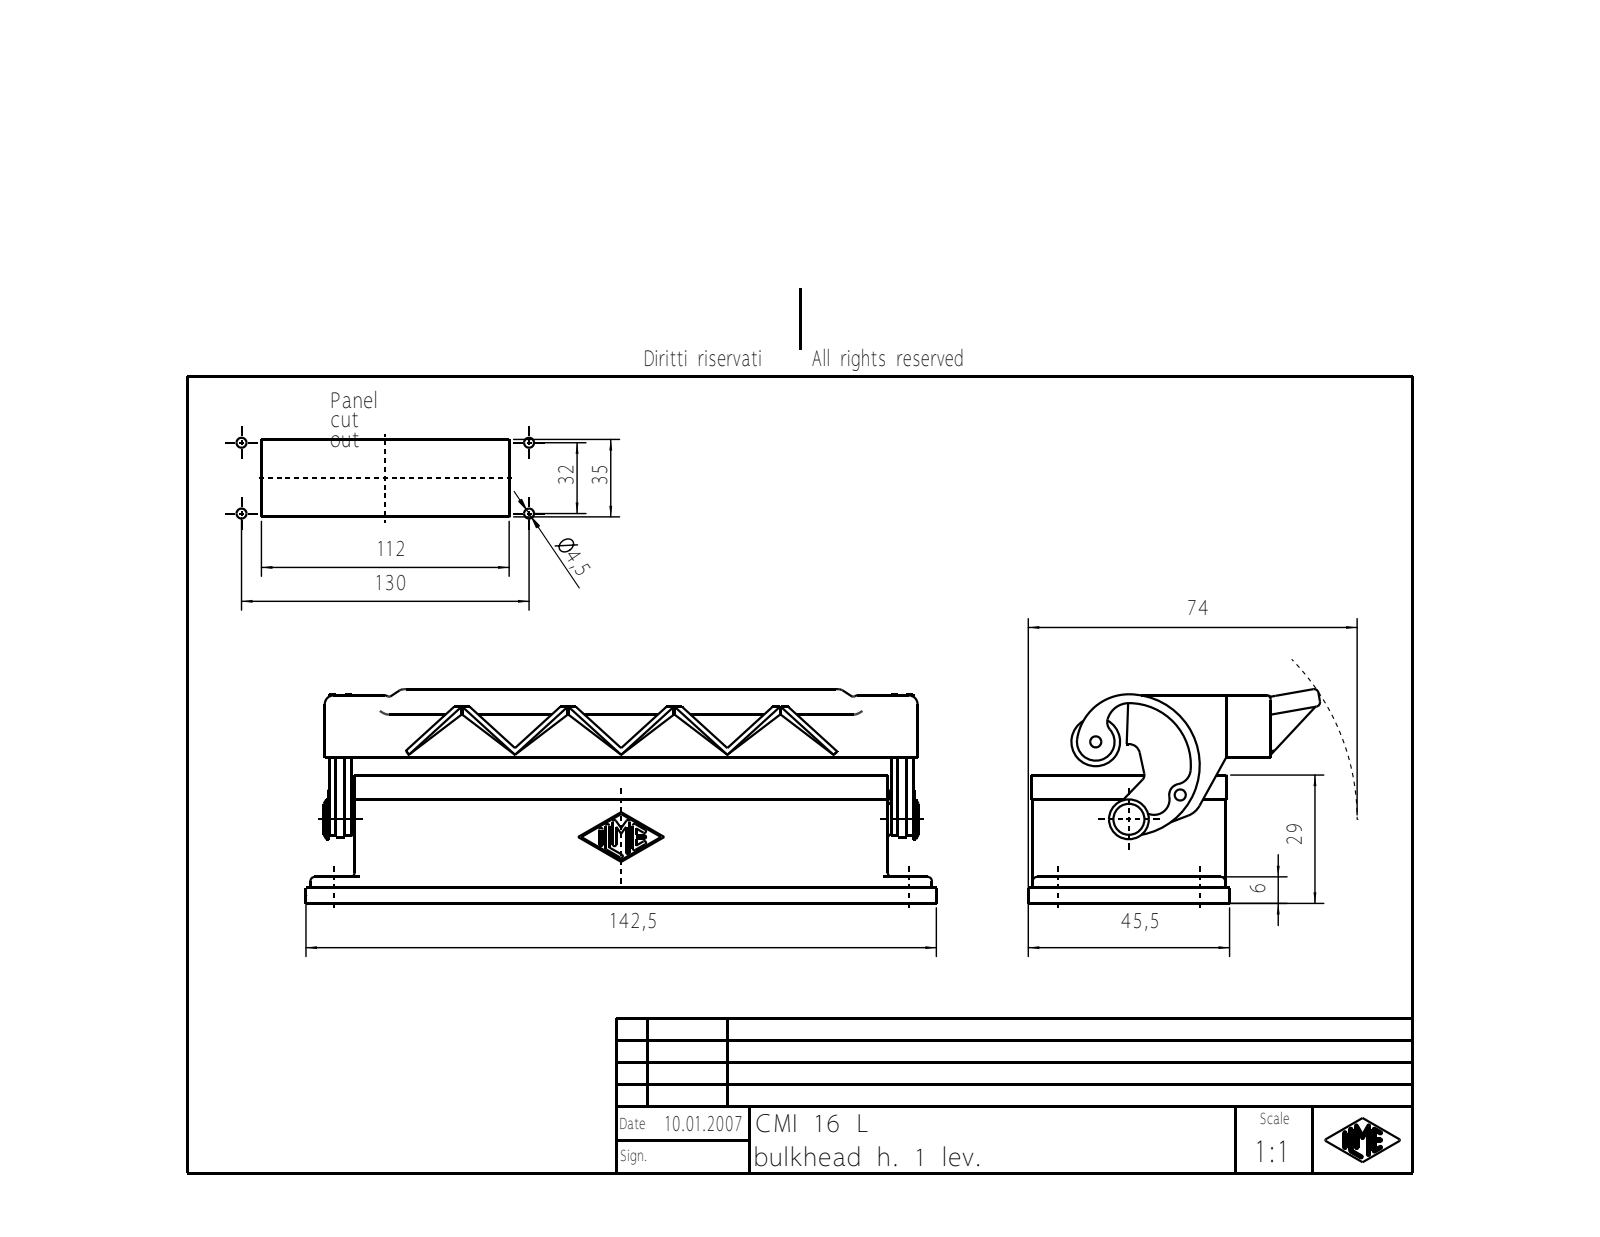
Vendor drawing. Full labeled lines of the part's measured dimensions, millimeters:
Part name (STEP PRODUCT): CMI 16 L
STEP written by: Autodesk Inventor 7 (AUTOMOTIVE_DESIGN)
Units: millimetres
Bodies: 4 solids, 490 faces (174 planar, 152 cylindrical, 164 other)
Overall size (bounding box): 142.5 × 65.95 × 48.42
Volume: 55 549 mm³ · Surface area: 39 412 mm²
Round holes (diameter × count): ⌀4.4 ×4, ⌀4.5 ×4, ⌀2 ×1
Round bosses / shafts (diameter × count): ⌀11 ×1, ⌀9 ×1, ⌀5 ×1, ⌀3 ×1, ⌀2.5 ×1
Partial cylindrical surfaces — rounded edges, fillets, slot ends (radius × count): R0.38 ×14, R1 ×13, R2 ×12, R6 ×8, R2.5 ×7, R5 ×6, R4 ×5, R3 ×4
Main face-to-face distances: 3, 4, 40.5, 1, 0.75, 43.5, 23.5, 40.75, 37.5, 39.75
Hole centre spacings: 32, 130, 133.88
